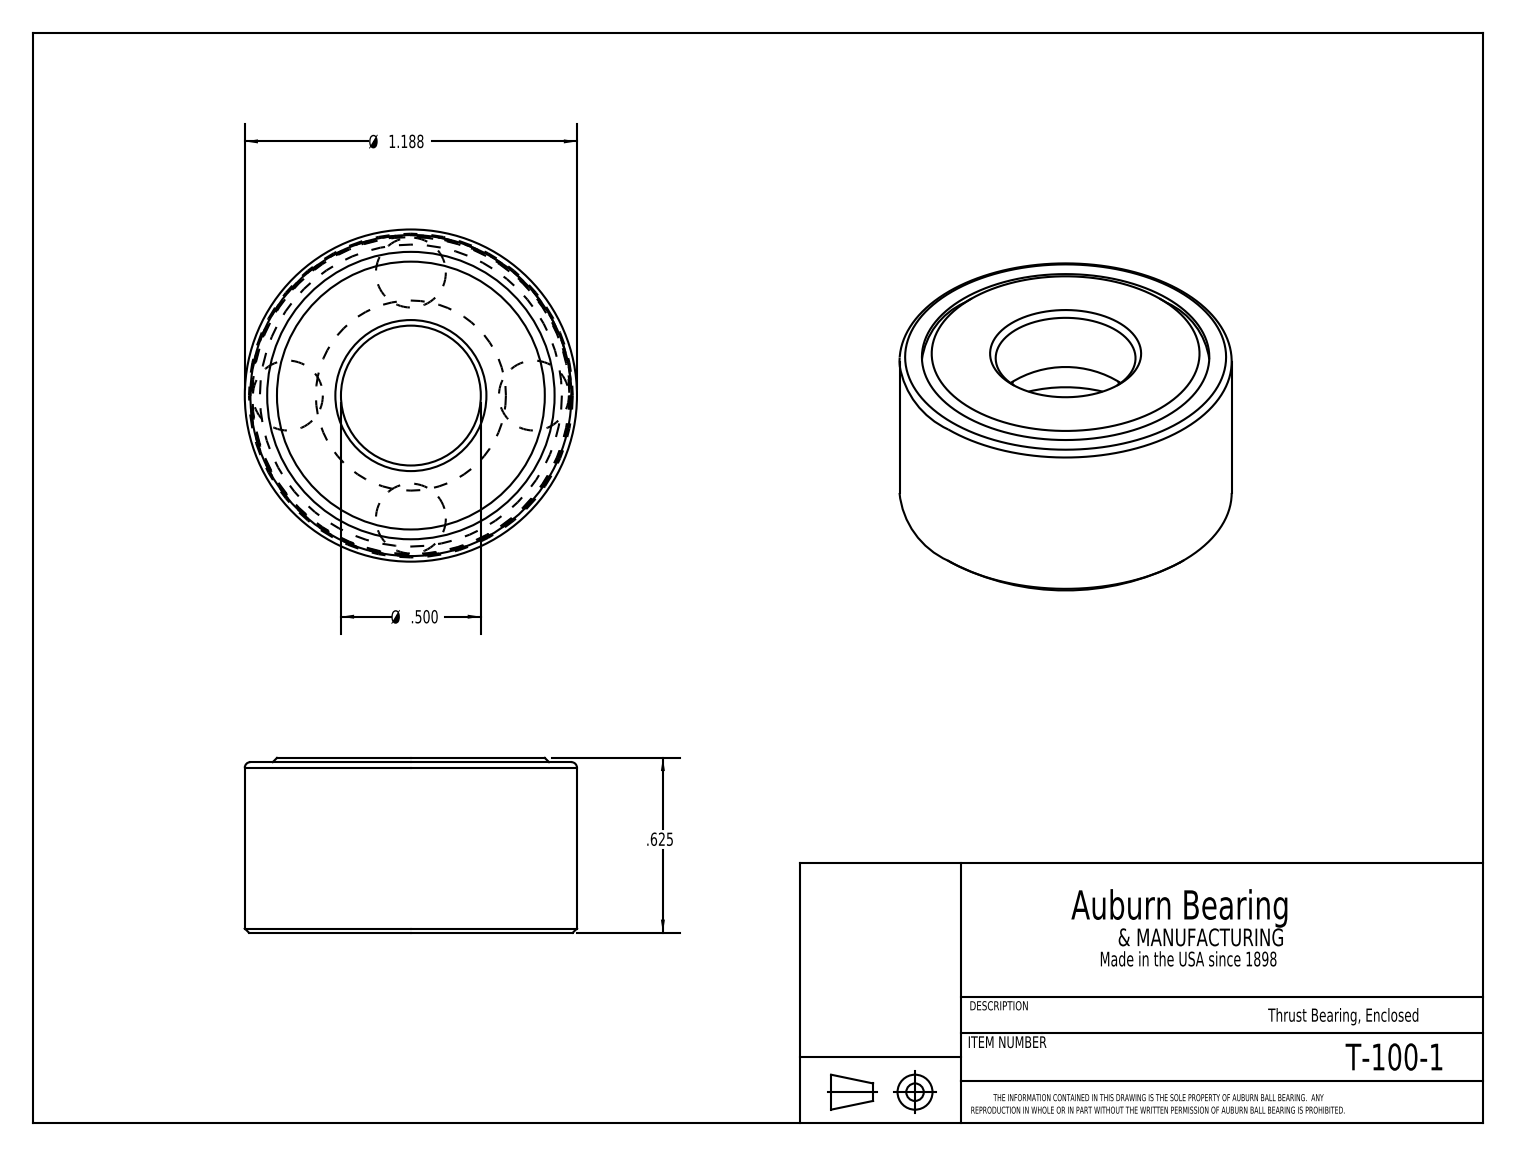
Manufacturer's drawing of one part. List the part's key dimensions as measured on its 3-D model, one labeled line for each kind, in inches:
Part name (STEP PRODUCT): T-100-1
STEP written by: SolidWorks 2016 (CONFIG_CONTROL_DESIGN)
Units: inches
Bodies: 6 solids, 28 faces (9 planar, 7 cylindrical, 12 other)
Overall size (bounding box): 1.188 × 1.188 × 0.625
Volume: 0.42 in³ · Surface area: 9.753 in²
Round holes (diameter × count): ⌀0.5 ×1, ⌀1.027 ×1, ⌀1.147 ×1
Round bosses / shafts (diameter × count): ⌀1.187 ×1, ⌀1.133 ×1
Main face-to-face distances: 0.625, 0.237, 0.388, 0.387, 0.15, 0.238, 0.61, 0.372, 0.222, 0.015
